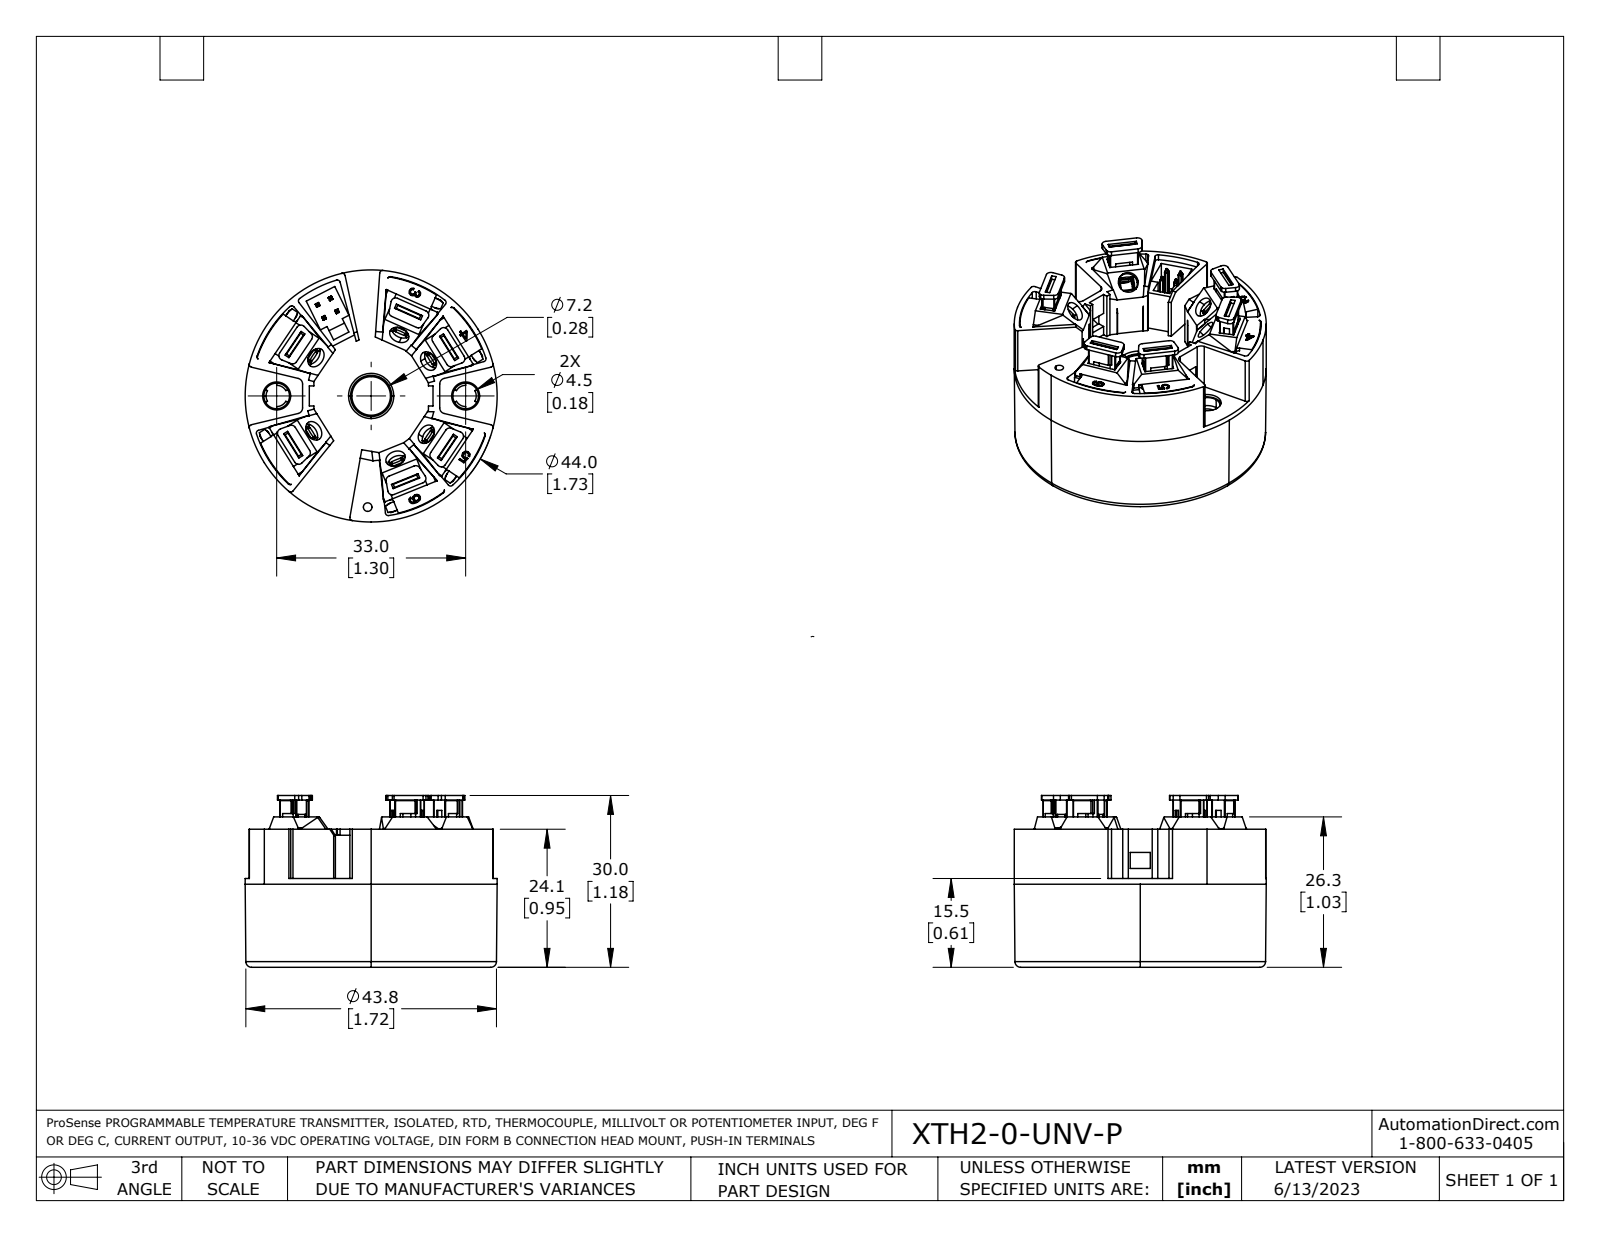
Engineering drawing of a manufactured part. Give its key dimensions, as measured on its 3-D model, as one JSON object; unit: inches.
{"part_name": "XTH2-0-UNV-P", "step_written_by": "SolidWorks 2021 (AUTOMOTIVE_DESIGN)", "units": "inches", "bodies": {"solids": 7, "faces": 3589, "planar": 1938, "cylindrical": 1032, "other": 619}, "overall_size": [1.732, 1.732, 1.181], "volume_in3": 0.663, "surface_area_in2": 36.3, "round_holes": [[0.053, 12], [0.043, 6], [0.138, 6], [0.193, 2], [0.248, 2], [0.059, 1], [0.213, 1], [0.283, 1], [0.339, 1], [1.594, 1], [1.646, 1]], "round_bosses_or_shafts": [[0.106, 12], [0.049, 12], [0.079, 6], [0.295, 2], [1.732, 1], [0.402, 1]], "partial_cylinders_radius": [[0.008, 184], [0.004, 150], [0.02, 76], [0.012, 66], [0.009, 28], [0.031, 24], [0.039, 22], [0.051, 18]], "face_to_face_distances": [0.039, 0.571, 0.61, 0.531, 0.028, 0.041, 0.024, 0.031, 0.03, 0.069], "hole_center_spacings": [0.635, 0.047, 0.553, 0.633, 0.084, 0.509, 0.743, 0.963]}
